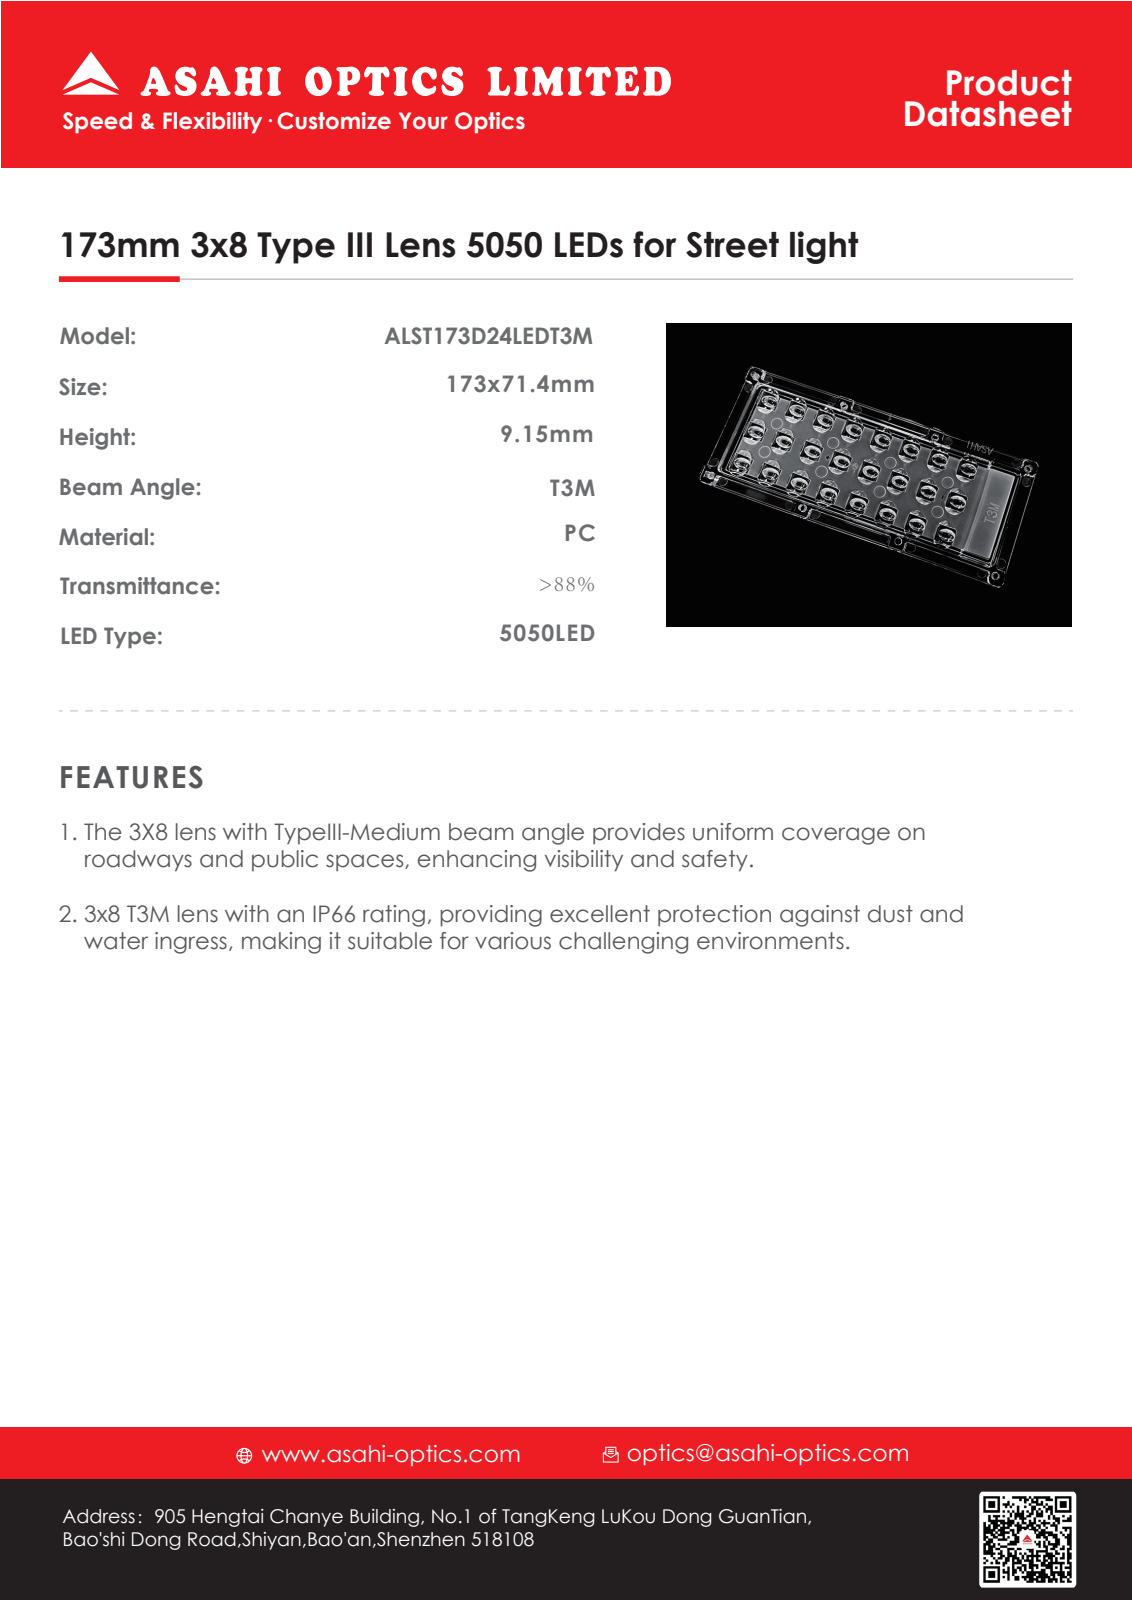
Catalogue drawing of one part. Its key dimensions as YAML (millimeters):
part_name: "24合1-T3M-NEW624_step"
step_written_by: "SIEMENS PLM Software NX 12.0 (AUTOMOTIVE_DESIGN)"
units: millimeters
bodies: {solids: 1, faces: 849, planar: 317, cylindrical: 152, other: 380}
overall_size: [173, 71.5, 9.51]
volume: 37501
surface_area: 33149
partial_cylinders:
  - {radius: 1, count: 28}
  - {radius: 0.5, count: 24}
  - {radius: 2, count: 24}
  - {radius: 3, count: 12}
  - {radius: 1.5, count: 4}
  - {radius: 4, count: 4}
  - {radius: 1.8, count: 2}
  - {radius: 2.5, count: 2}
face_to_face_distances: [2.2, 1.5, 3.7, 2.65, 1.15, 1.05, 0.5, 1.7, 2.5, 2]
